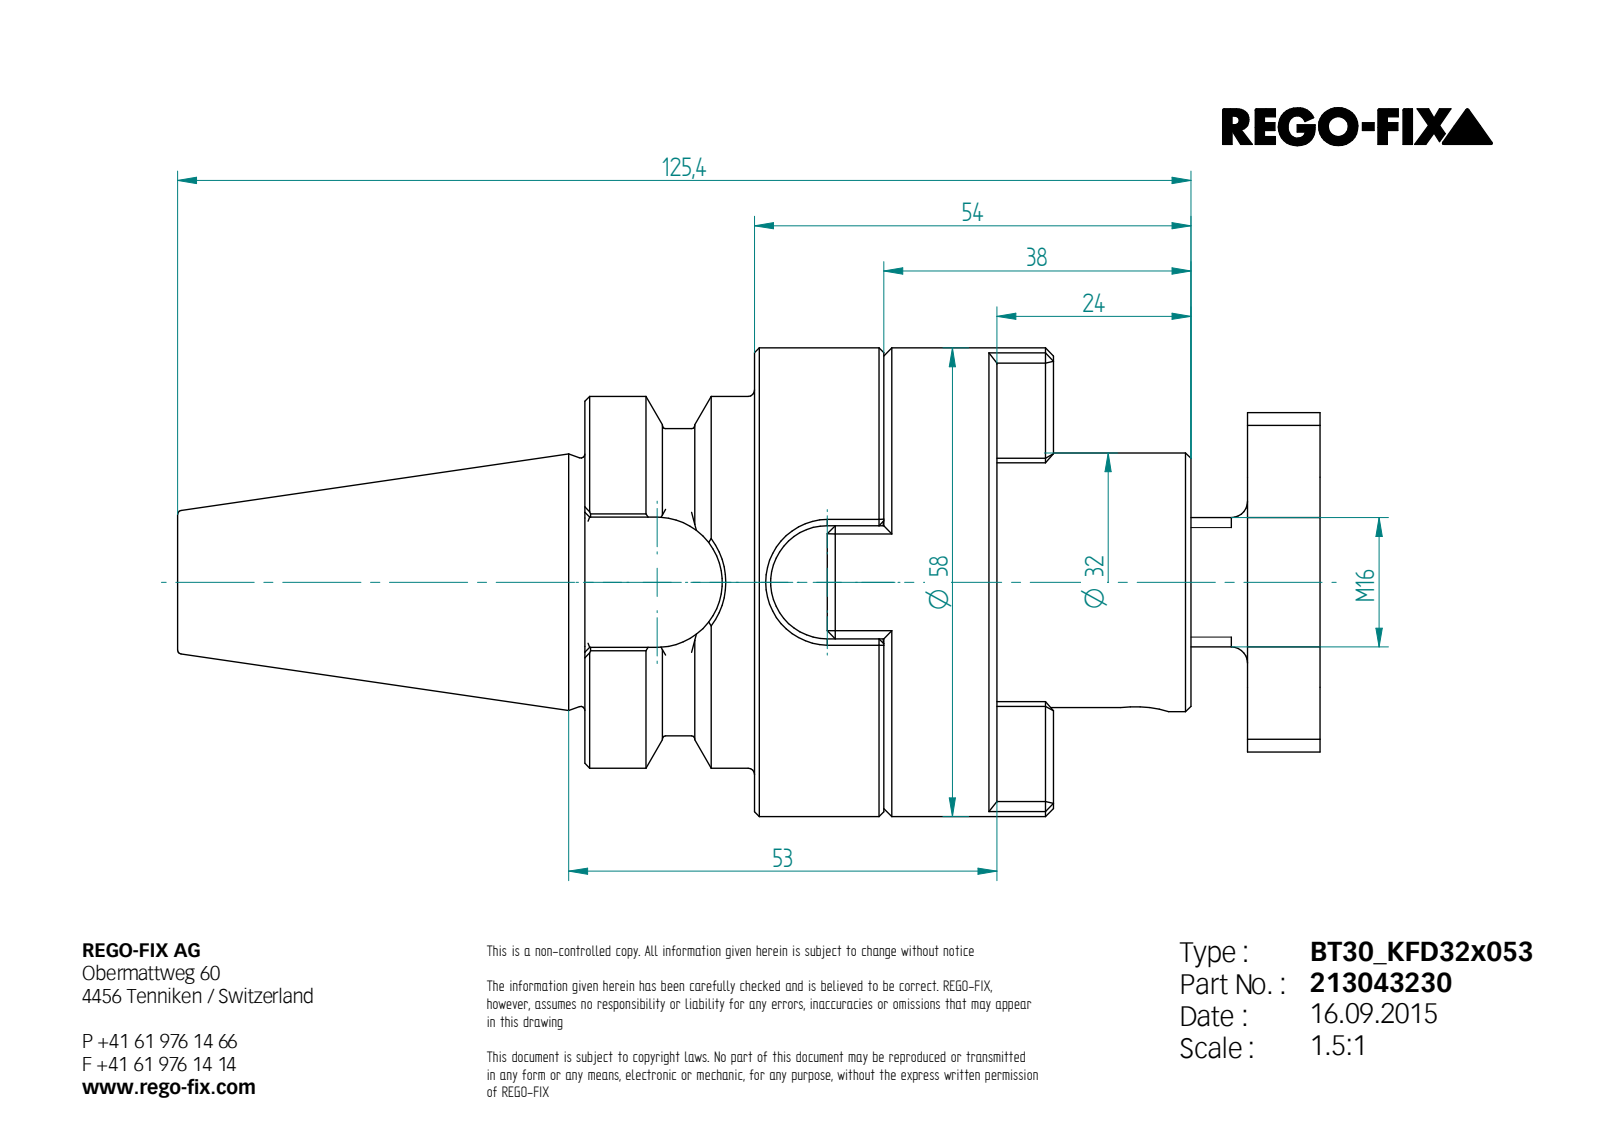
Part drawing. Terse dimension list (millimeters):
written by: Unknown (AUTOMOTIVE_DESIGN)
unit: mm
bodies: 3 solids, 217 faces (120 planar, 39 cylindrical, 58 other)
size: 141.4 × 58 × 58
volume: 154 087 mm³; area: 37 147 mm²
holes: 1× ⌀10.11, 1× ⌀12.5, 1× ⌀13.84, 1× ⌀17, 1× ⌀32
bosses: 1× ⌀58, 1× ⌀46, 1× ⌀31.4, 1× ⌀16
rounds: 8× R0.5, 4× R5, 2× R4, 1× R7, 1× R8.05, 1× R19, 1× R21
face distances: 14, 54, 16, 21, 40, 9, 45, 30, 61, 7
